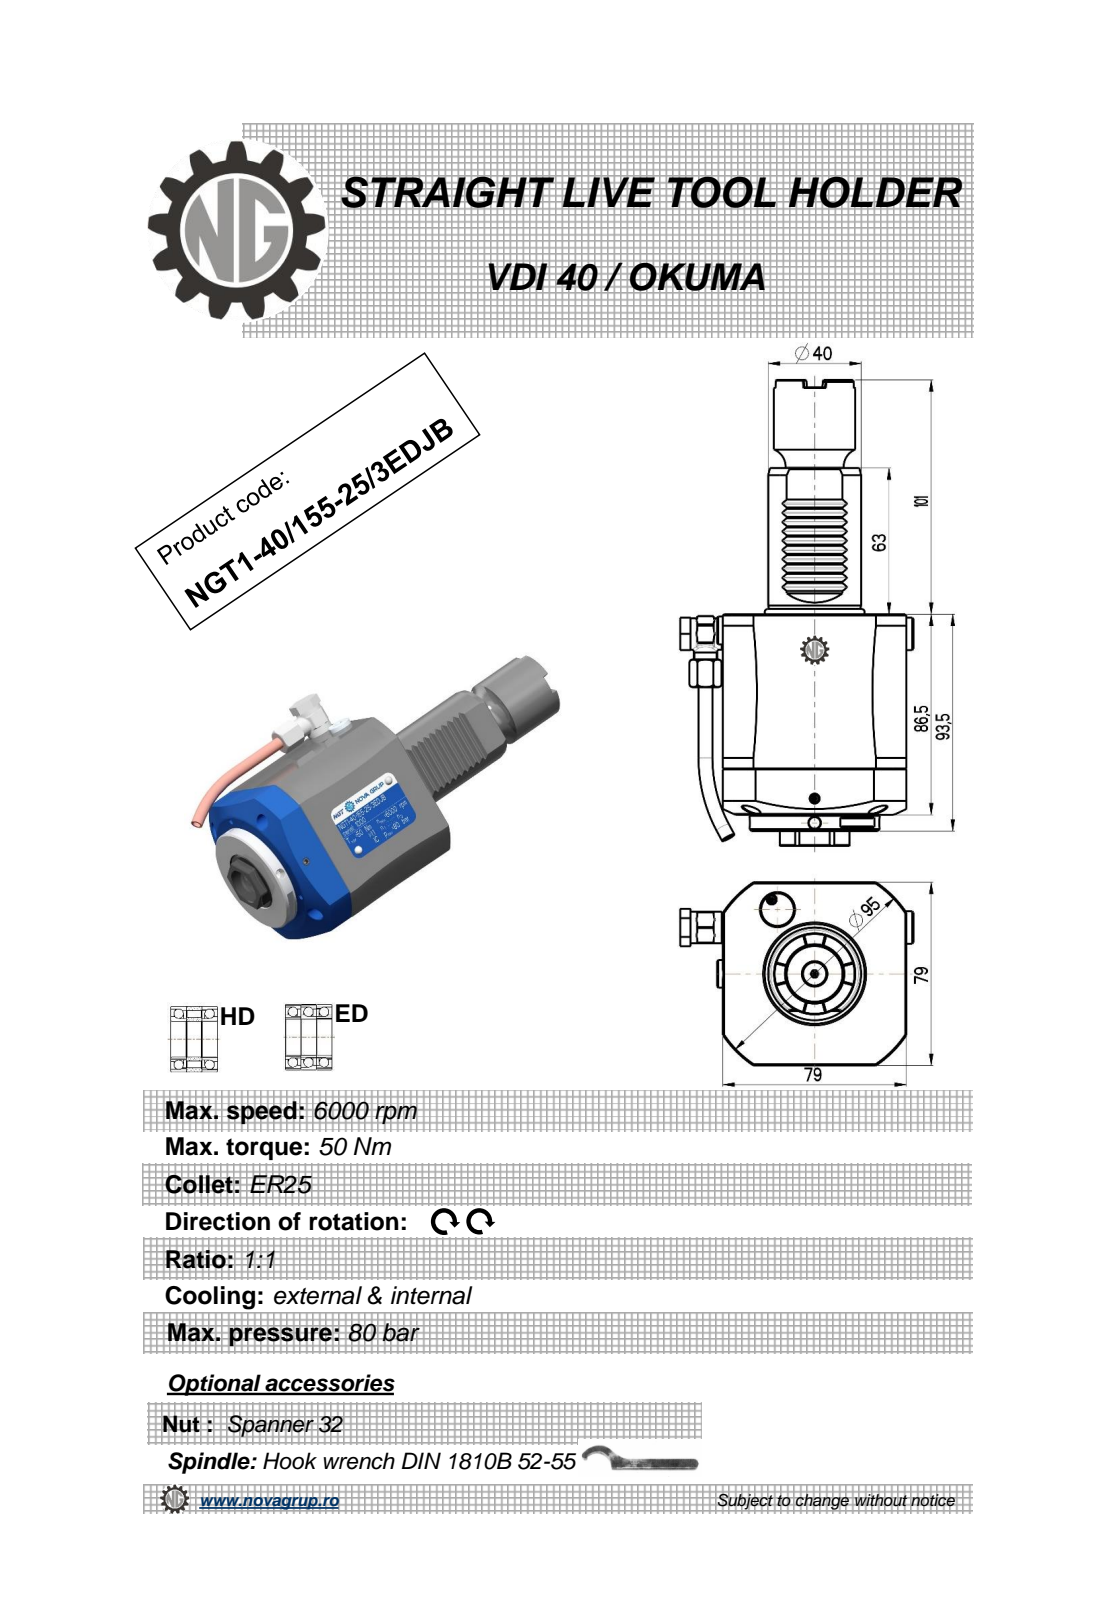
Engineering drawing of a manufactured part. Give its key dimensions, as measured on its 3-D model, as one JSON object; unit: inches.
{"part_name": "NGT1_40_155_25_3HDJB", "step_written_by": "PRO/ENGINEER BY PARAMETRIC TECHNOLOGY CORPORATION, 2010280 (CONFIG_CONTROL_DESIGN)", "units": "inches", "bodies": {"solids": 2, "faces": 433, "planar": 167, "cylindrical": 109, "other": 157}, "overall_size": [7.913, 3.953, 3.11], "volume_in3": 38.56, "surface_area_in2": 89.56, "round_holes": [[0.157, 3], [0.197, 2], [0.118, 1], [0.236, 1], [0.244, 1], [0.354, 1], [0.394, 1], [0.433, 1], [0.709, 1], [0.984, 1], [1.043, 1]], "round_bosses_or_shafts": [[2.205, 1], [1.575, 1], [1.378, 1], [0.551, 1], [0.535, 1], [0.512, 1], [0.472, 1], [0.394, 1]], "partial_cylinders_radius": [[0.012, 10], [0.016, 6], [0.02, 4], [0.303, 1], [0.591, 1], [1.85, 1], [1.87, 1]], "face_to_face_distances": [3.11, 3.406, 0.276, 3.681, 0.111, 6.161, 5.886, 2.48, 0.334, 0.557], "hole_center_spacings": [0.016, 2.011, 2.026, 3.304]}
